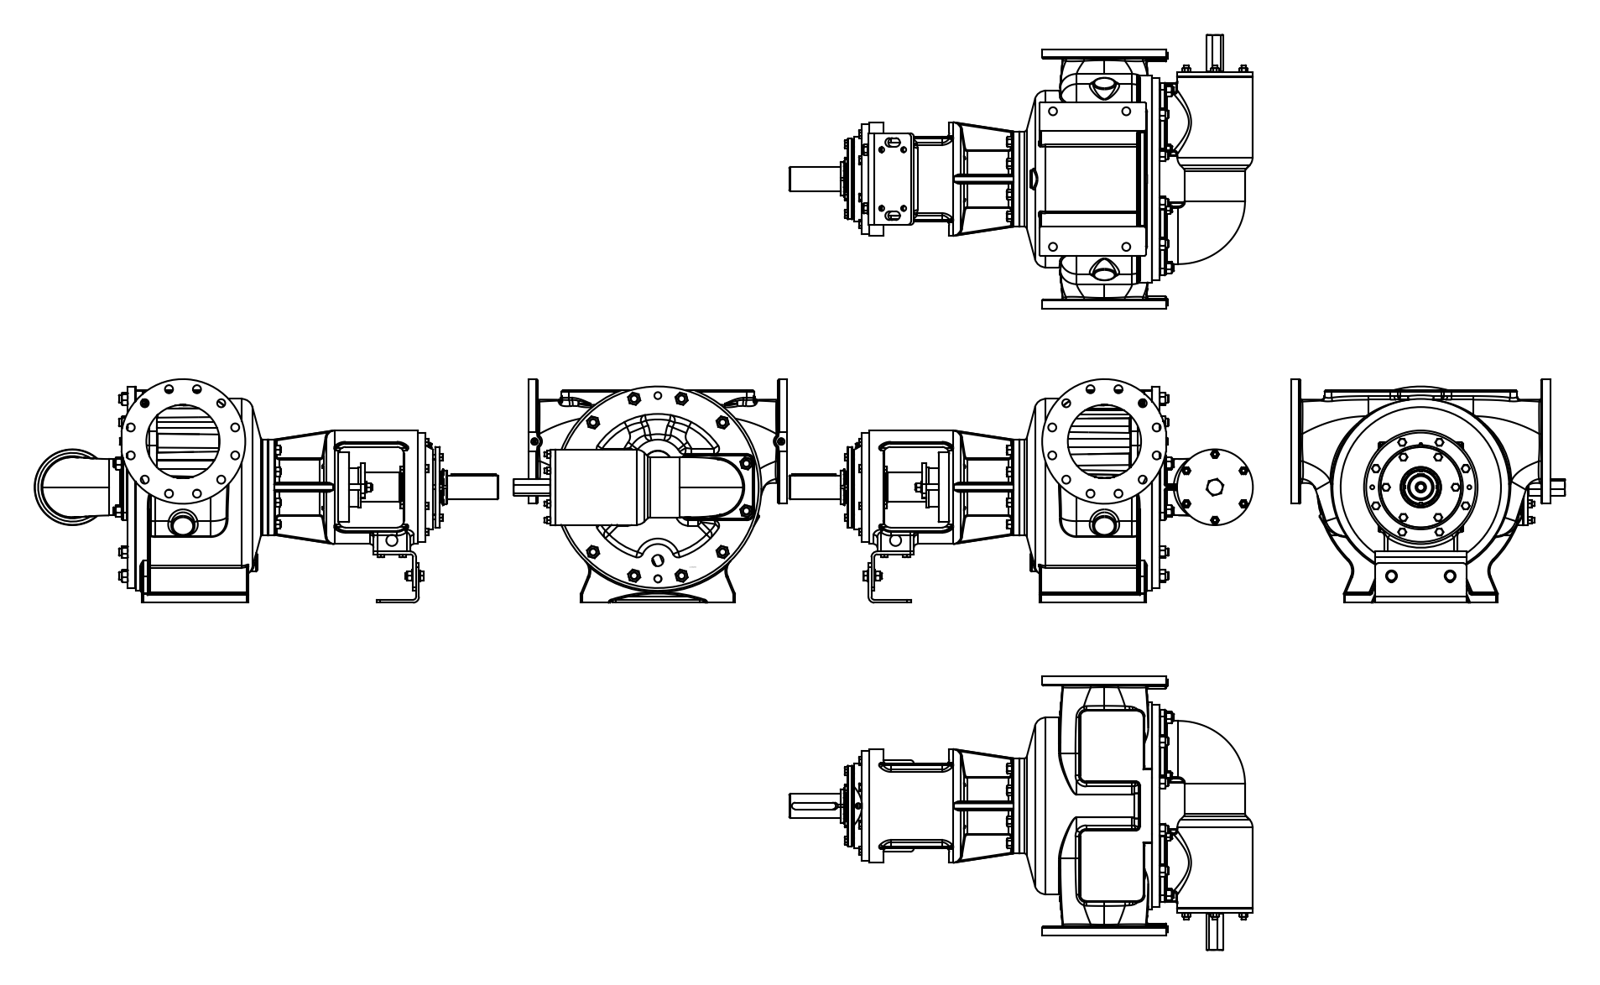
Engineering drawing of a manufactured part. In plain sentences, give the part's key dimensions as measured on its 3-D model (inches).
The part is named "R200_A_Y_POS_7". Its 3-D file was written by "CREO PARAMETRIC BY PTC INC, 2017110 (CONFIG_CONTROL_DESIGN)". It is 2 solids with 1375 faces: 289 planar, 461 cylindrical and 625 other. Overall it measures 49.803 by 29.39 by 24.291 inches. Its volume is 8 348 cubic inches and its surface area 4 534 square inches. Round holes: 21 of diameter 0.866, 16 of diameter 0.551, 6 of diameter 0.531, 3 of diameter 0.748, 2 of diameter 0.433, 2 of diameter 0.472, 1 of diameter 0.827, 1 of diameter 1.024, 1 of diameter 2.559, 1 of diameter 2.67, 1 of diameter 3.543, 1 of diameter 4.331. Round bosses or shafts: 6 of diameter 0.709, 6 of diameter 0.472, 2 of diameter 6.063, 1 of diameter 22.244, 1 of diameter 21.89, 1 of diameter 18.976, 1 of diameter 13.386, 1 of diameter 12.205. Partial cylindrical surfaces (rounded edges, fillets, slot ends): 86 of radius 0.157, 28 of radius 0.394, 24 of radius 0.118, 14 of radius 0.787, 9 of radius 0.591, 8 of radius 0.374, 8 of radius 0.472, 7 of radius 1.772. The main face-to-face distances are 0.984, 0.827, 27.795, 26.811, 2.382, 32.126, 0.787, 0.315, 1.26, 31.299. The hole center spacings are 3.74, 9.843, 3.543, 6.305, 3.006, 5.807, 8.212, 10.058.
